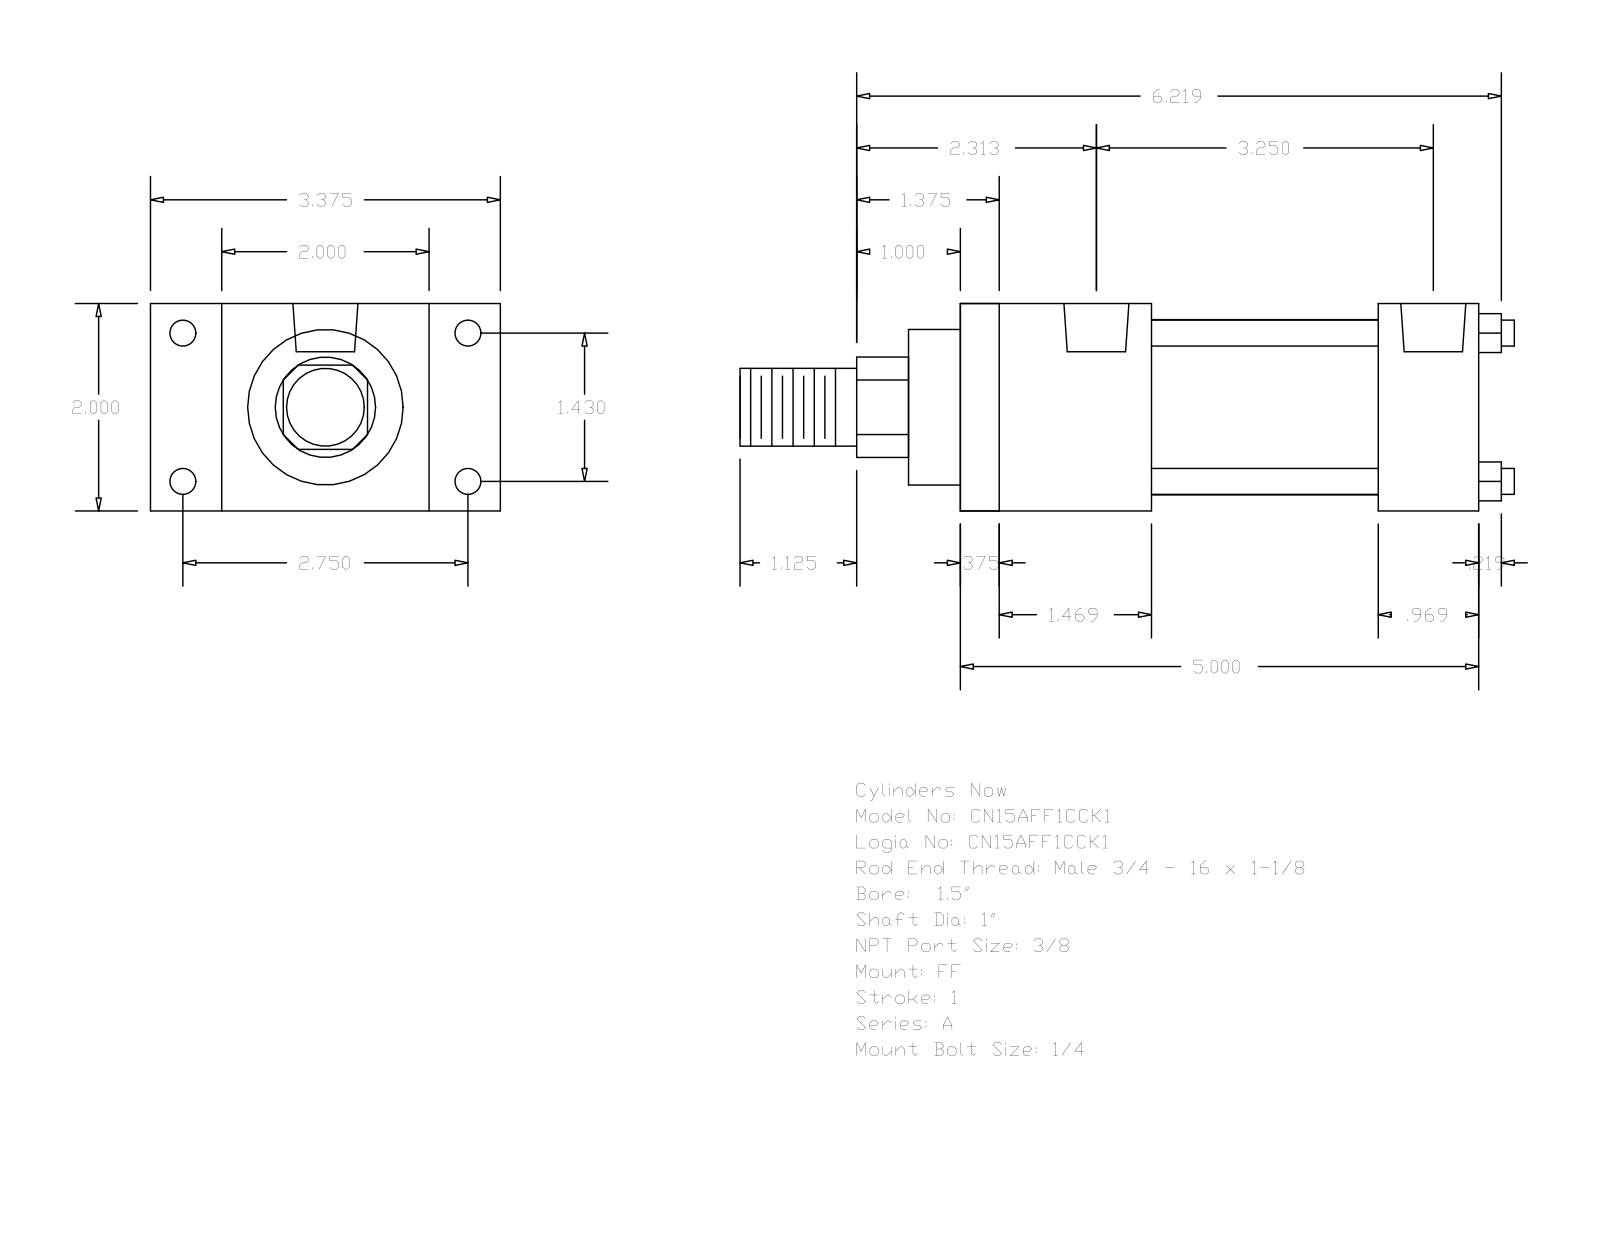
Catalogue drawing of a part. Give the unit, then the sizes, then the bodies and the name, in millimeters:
Units: millimetres
Overall size (bounding box): 189.71 × 85.72 × 50.8
Round holes (diameter × count): ⌀5.56 ×4, ⌀6.35 ×4, ⌀15.93 ×2
Round bosses / shafts (diameter × count): ⌀6.35 ×4, ⌀42.93 ×1, ⌀38.1 ×1, ⌀25.4 ×1, ⌀19.05 ×1
Partial cylindrical surfaces — rounded edges, fillets, slot ends (radius × count): R12.29 ×1
Main face-to-face distances: 50.8, 127, 9.52, 117.48, 46.83, 102.39, 37.31, 92.87, 55.56, 80.17
Hole centre spacings: 3.97, 36.32, 69.84, 74.61, 78.58, 78.72, 82.55
Bodies: 0 solids, 92 faces (64 planar, 28 cylindrical, 0 other)
Part name (STEP PRODUCT): A_FF__0150_1
STEP written by: GSSL Pune (CONFIG_CONTROL_DESIGN)
